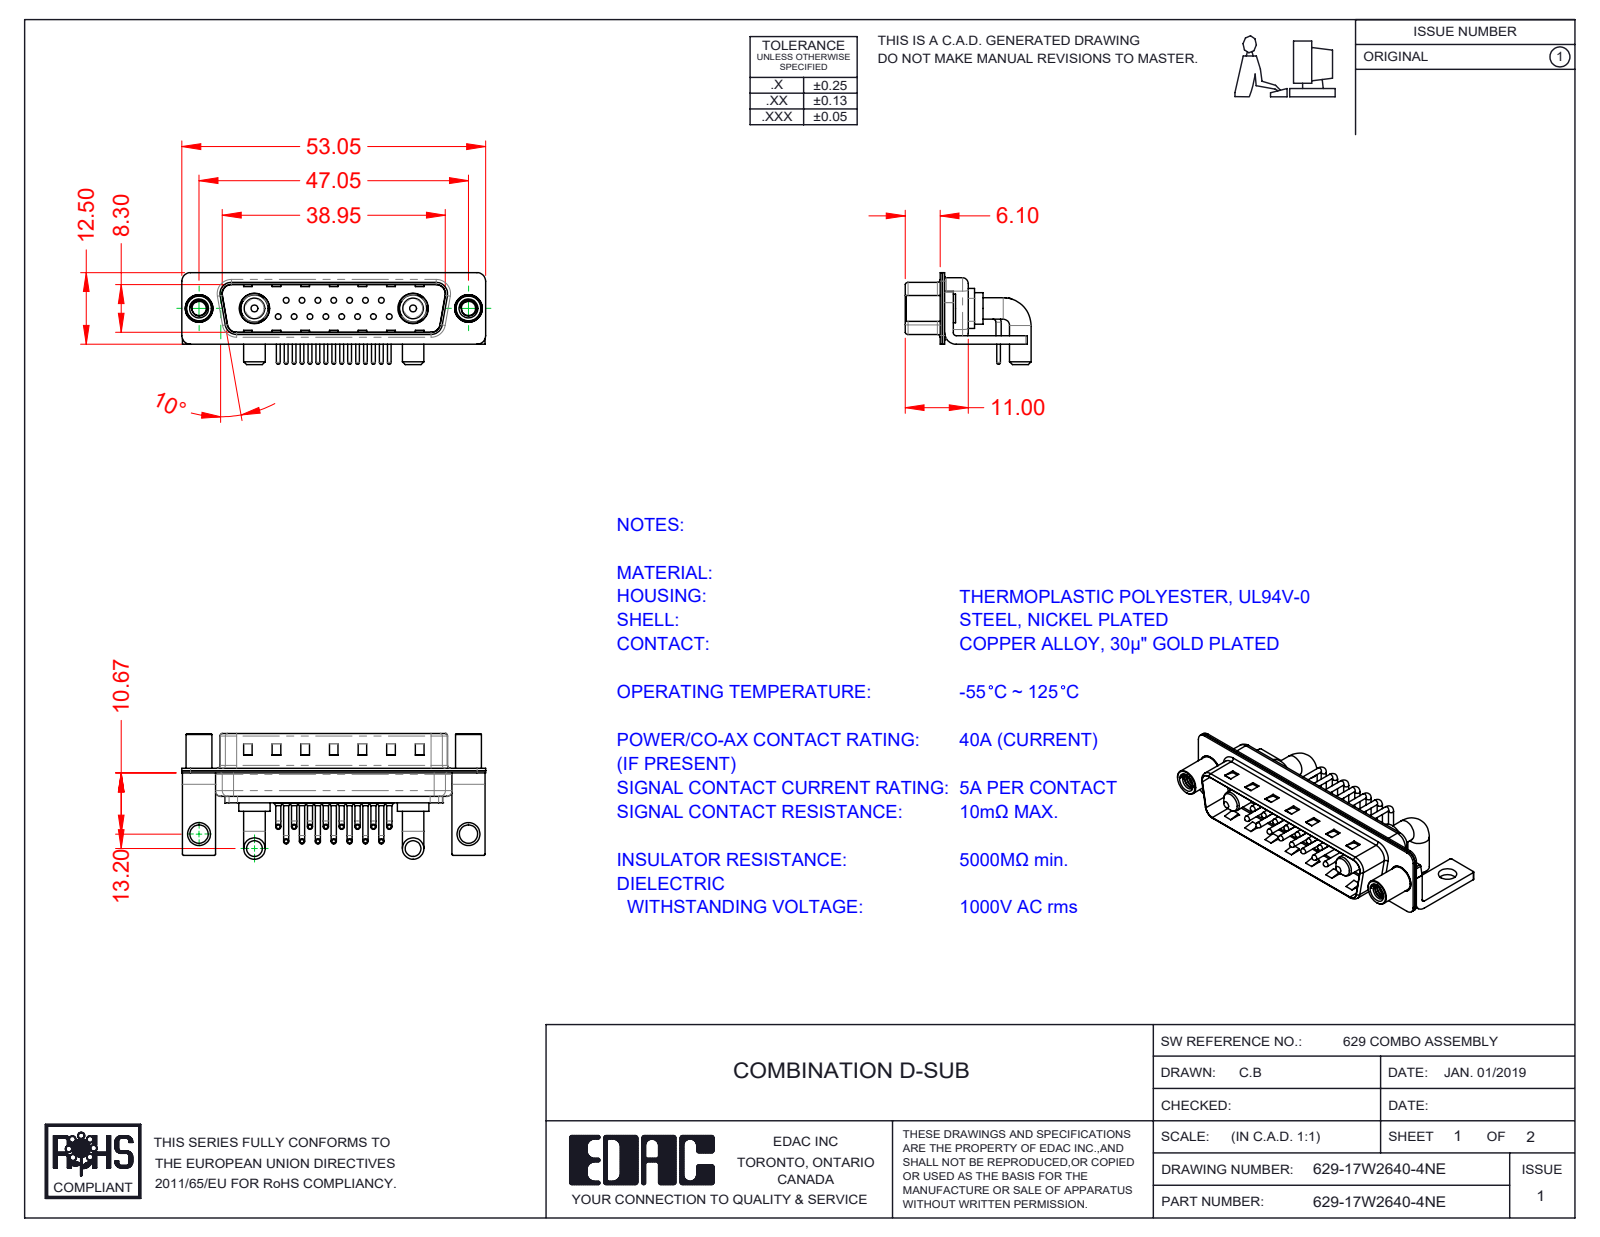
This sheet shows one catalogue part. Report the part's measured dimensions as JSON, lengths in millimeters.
{"part_name": "629Combo Shell Rear_25 Contacts; 629Combo Housing_17W2; Power Pin_40A RA; 629Combo Stabilizer Bracket (+5 more)", "step_written_by": "SolidWorks 2020 (CONFIG_CONTROL_DESIGN)", "units": "millimeters", "bodies": {"solids": 26, "faces": 2210, "planar": 1173, "cylindrical": 791, "other": 246}, "overall_size": [53.05, 21.98, 16.05], "volume_mm3": 3642, "surface_area_mm2": 8488, "round_holes": [[0.75, 15], [1.6, 15], [2, 15], [2.5, 2], [3.2, 2], [4, 2], [4.8, 2], [4.85, 2], [5.3, 2]], "round_bosses_or_shafts": [[0.9, 30], [1.5, 15], [1, 15], [0.65, 15], [3.75, 4], [5.5, 2], [5.2, 2], [5, 2]], "partial_cylinders_radius": [[0.25, 16], [1.5, 16], [1.01, 15], [2, 13], [0.5, 9], [1.6, 8], [0.6, 4], [0.65, 4]], "face_to_face_distances": [0.4, 0.8, 9.5, 1.5, 9.1, 8.7, 9.9, 0.6, 0.75, 5.2], "hole_center_spacings": [3.16, 2.77, 5.54, 8.31, 5.04, 7.49, 11.08, 5.03]}
